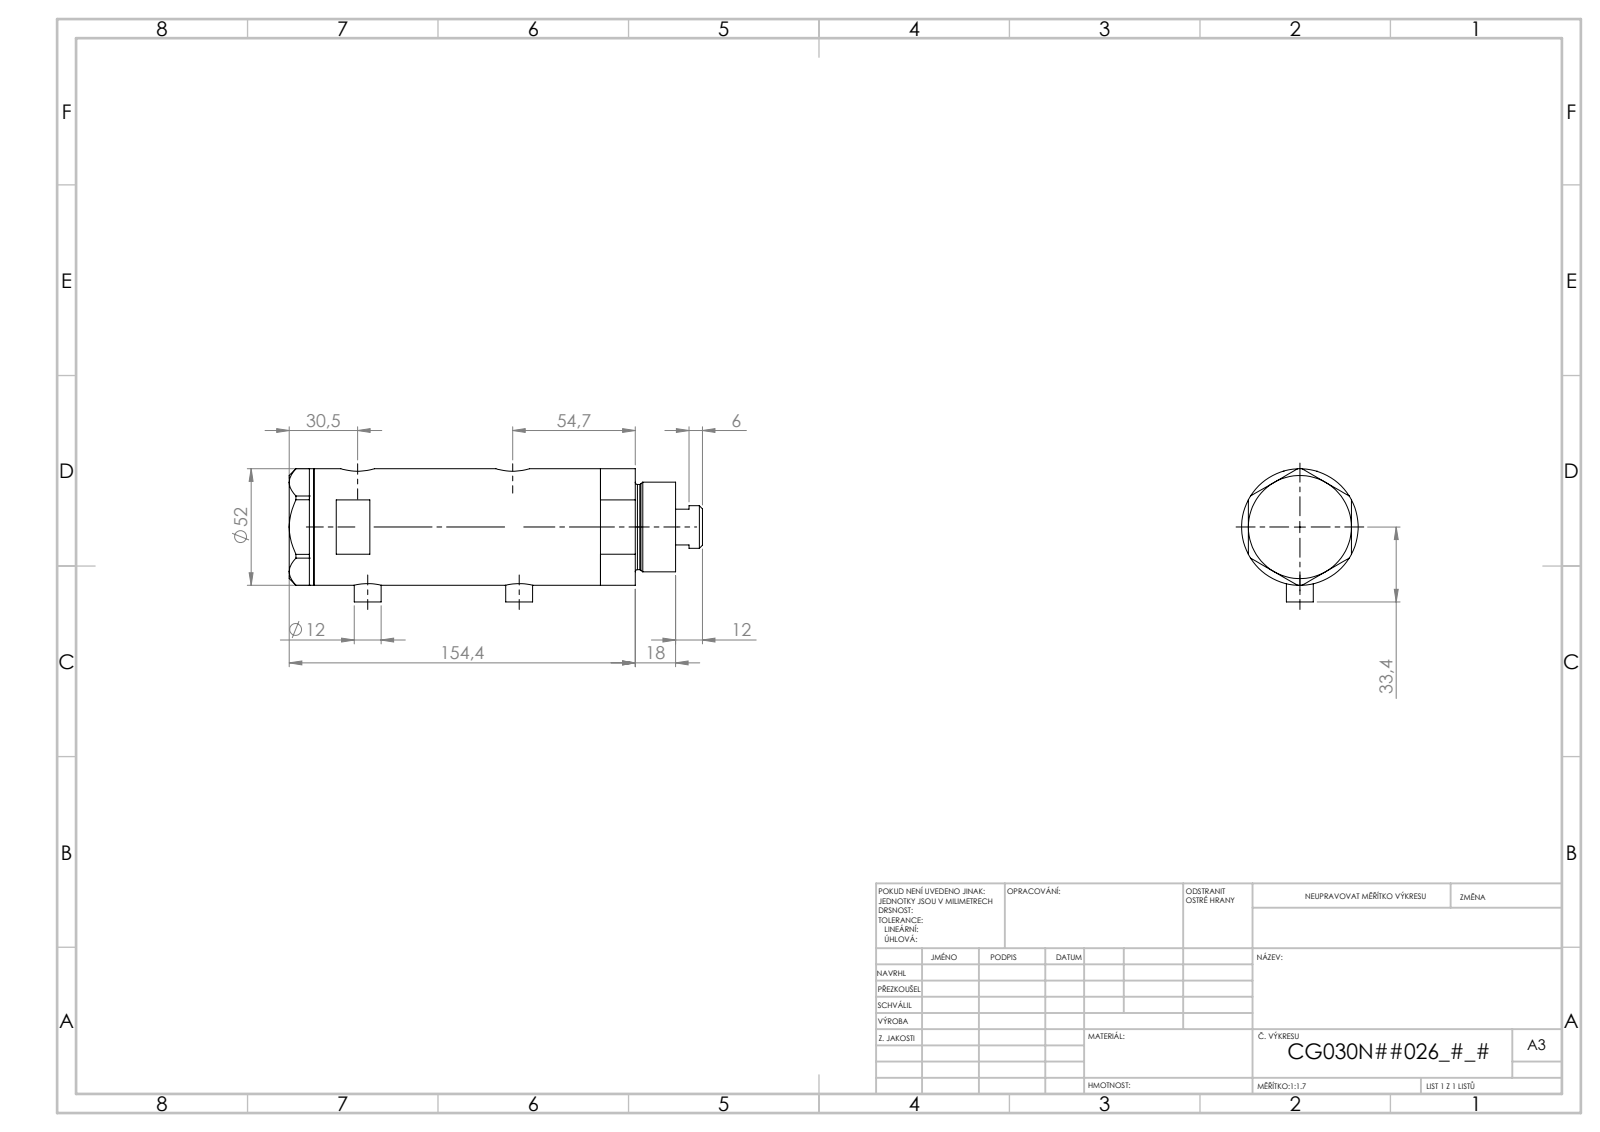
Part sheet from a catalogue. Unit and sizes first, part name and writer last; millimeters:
Units: millimetres
Overall size (bounding box): 175.02 × 53.1 × 52
Round holes (diameter × count): ⌀5 ×2, ⌀9.73 ×2, ⌀12.5 ×2, ⌀15 ×2, ⌀6.5 ×1, ⌀20 ×1, ⌀21.5 ×1, ⌀30 ×1, ⌀33 ×1, ⌀44 ×1
Round bosses / shafts (diameter × count): ⌀12 ×2, ⌀52 ×1, ⌀40 ×1, ⌀38 ×1, ⌀19 ×1
Main face-to-face distances: 23.81, 10.99, 34.8, 46, 90.55, 79.56, 55.75, 126.95, 115.96, 92.15
Hole centre spacings: 2.9, 4.5, 52.75, 55.65, 57.25, 60.15, 2.89, 2.91
Volume: 312 525 mm³ · Surface area: 73 421 mm²
Bodies: 4 solids, 140 faces (67 planar, 53 cylindrical, 20 other)
Part name (STEP PRODUCT): V270CG_VC; V270CG_MIDDLE; V270CG_BACK; V270CG_FRONT
STEP written by: SolidWorks 2019 (CONFIG_CONTROL_DESIGN)
